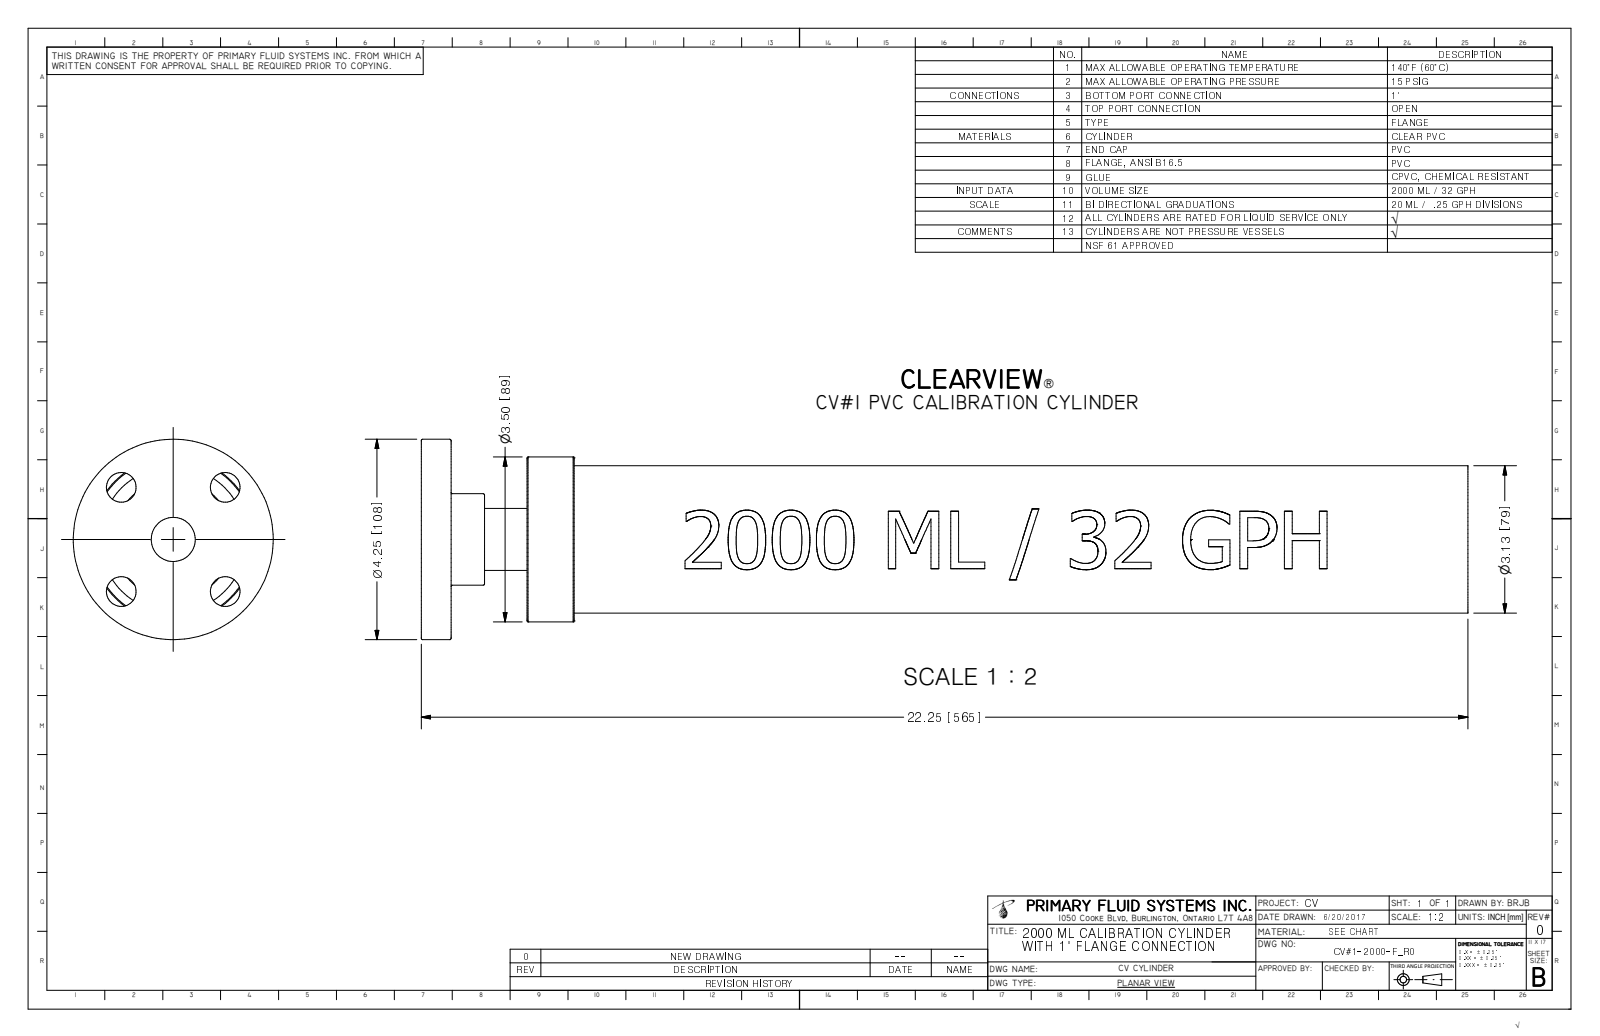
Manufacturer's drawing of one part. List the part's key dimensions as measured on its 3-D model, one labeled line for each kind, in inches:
Part name (STEP PRODUCT): PV#1-2000-F_R0
STEP written by: Autodesk Inventor 2009 (AUTOMOTIVE_DESIGN)
Units: inches
Bodies: 1 solid, 275 faces (86 planar, 31 cylindrical, 158 other)
Overall size (bounding box): 22.25 × 4.25 × 4.25
Volume: 28.04 in³ · Surface area: 484.7 in²
Round holes (diameter × count): ⌀0.63 ×4, ⌀0.936 ×1, ⌀0.957 ×1, ⌀1.156 ×1, ⌀3.005 ×1, ⌀3.156 ×1
Round bosses / shafts (diameter × count): ⌀4.25 ×1, ⌀3.5 ×1, ⌀3.125 ×1, ⌀2.996 ×1, ⌀1.941 ×1, ⌀1.315 ×1
Partial cylindrical surfaces — rounded edges, fillets, slot ends (radius × count): R1.561 ×1
Main face-to-face distances: 0.635, 2.25, 1.615, 3.25, 2.615, 1, 1.345, 0.71, 0.905, 1.905
Hole centre spacings: 1.562, 2.209, 3.125
